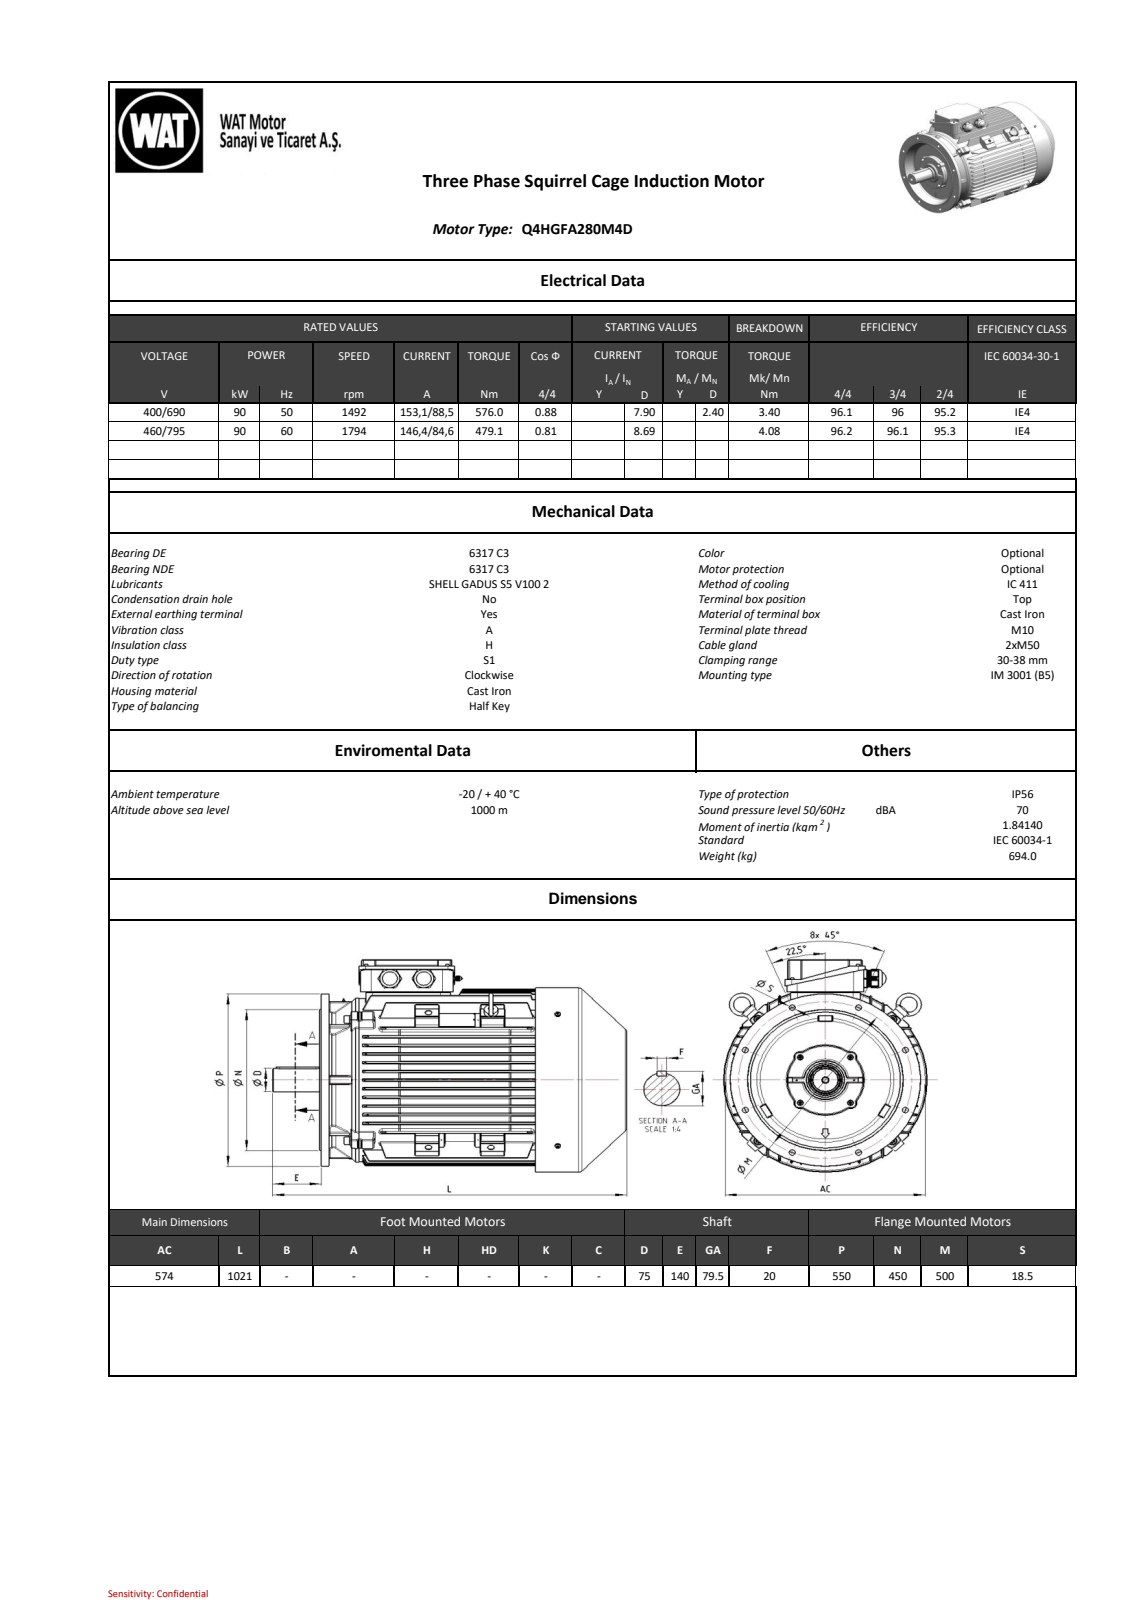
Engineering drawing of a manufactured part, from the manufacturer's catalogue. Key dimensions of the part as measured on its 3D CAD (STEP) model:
Part name (STEP PRODUCT): AB_objects
STEP written by: SIEMENS PLM Software NX2206.8101 (AUTOMOTIVE_DESIGN)
Units: millimetres
Bodies: 0 solids, 3650 faces (1451 planar, 968 cylindrical, 1231 other)
Overall size (bounding box): 1021.04 × 678.21 × 588
Round holes (diameter × count): ⌀18.5 ×14, ⌀14.75 ×4, ⌀10 ×1, ⌀18 ×1, ⌀21 ×1, ⌀585 ×1
Round bosses / shafts (diameter × count): ⌀27.4 ×4, ⌀23.67 ×4, ⌀16 ×4, ⌀15.73 ×4, ⌀10 ×4, ⌀58 ×2, ⌀55.1 ×2, ⌀52.3 ×2
Partial cylindrical surfaces — rounded edges, fillets, slot ends (radius × count): R1.5 ×342, R3 ×83, R1 ×54, R5 ×24, R0.2 ×17, R2 ×12, R2.18 ×12, R0.5 ×8
Main face-to-face distances: 23, 30, 53, 828.04, 858.04, 881.04, 296.44, 262.14, 243.68, 307.6
Hole centre spacings: 104.7, 191.34, 250, 291.49, 353.55, 435.47, 461.94, 513.46
